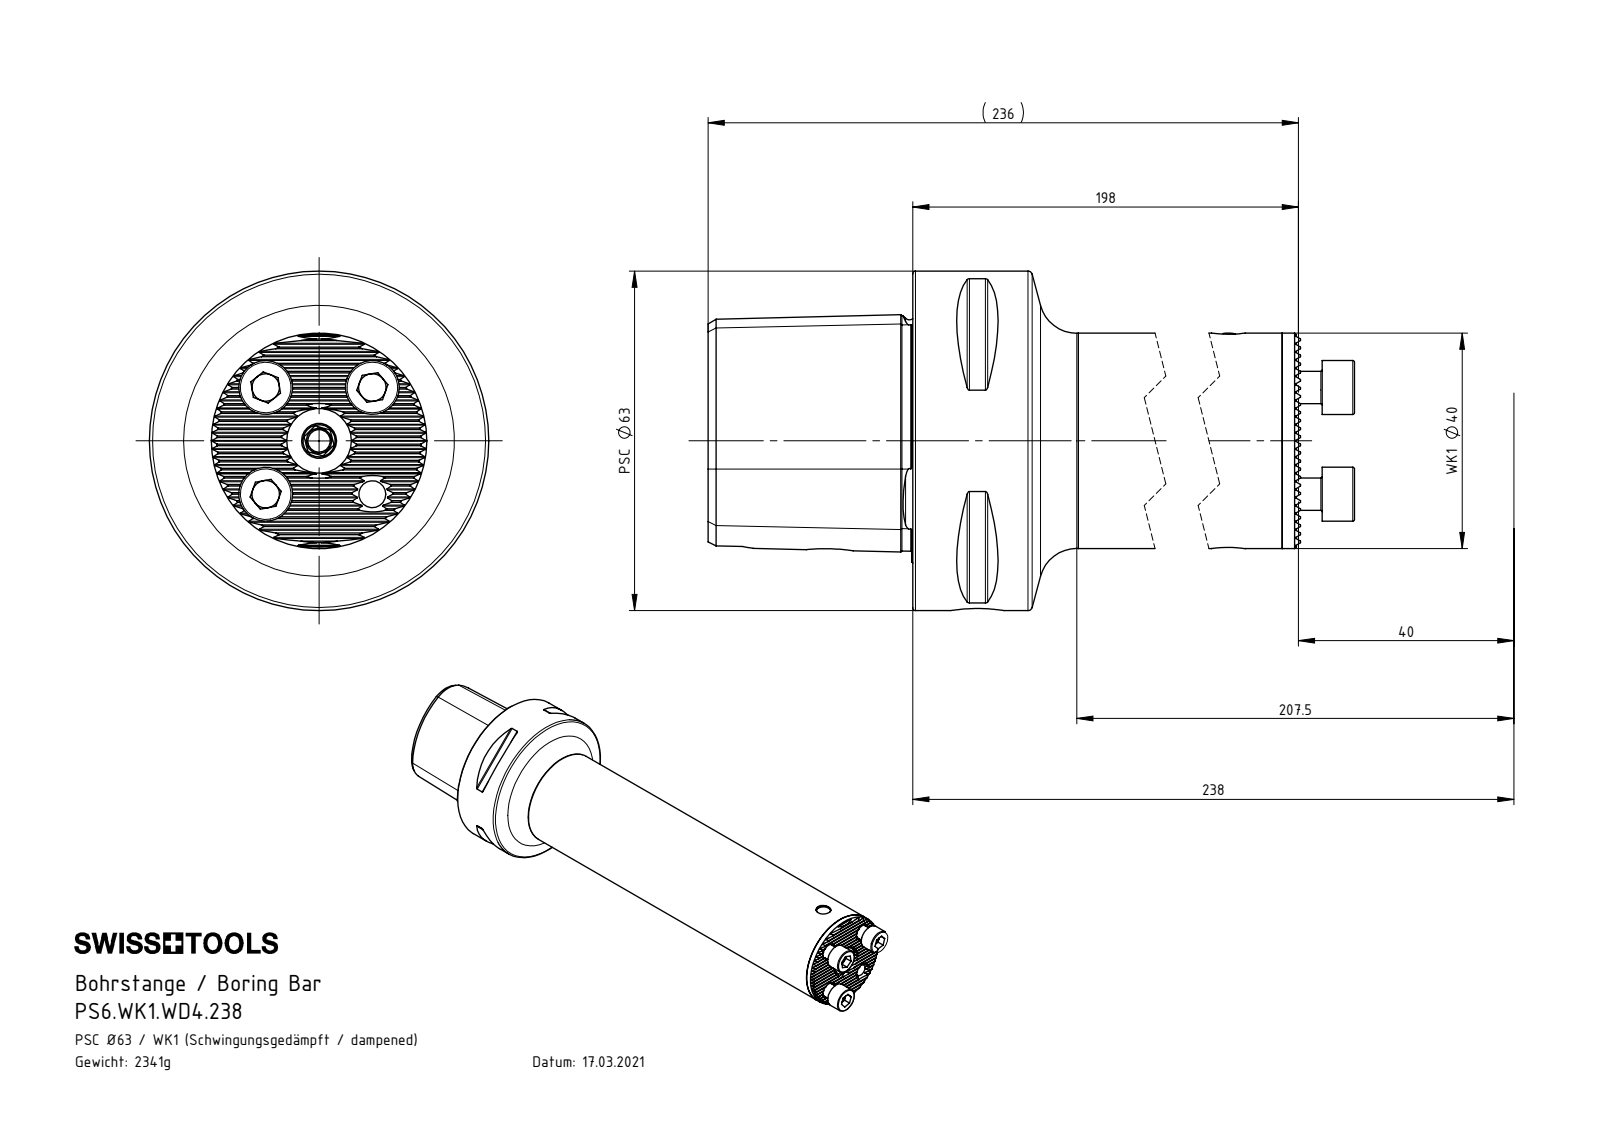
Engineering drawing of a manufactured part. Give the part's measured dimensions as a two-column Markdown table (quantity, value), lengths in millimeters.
| quantity | value |
| --- | --- |
| part name | ISO 4762 - M6 x 16; WD4-BG1.035.100; PS6.WK1.WD4.238; WD4-ER1.035.019_A (+8 more) |
| STEP written by | SolidWorks 2017 (AUTOMOTIVE_DESIGN) |
| units | millimeters |
| bodies | 16 solids, 532 faces (267 planar, 120 cylindrical, 145 other) |
| overall size | 246.4 × 63 × 63 |
| volume | 302 737 mm³ |
| surface area | 94 058 mm² |
| round holes (diameter × count) | 5 × 4, 6 × 2, 4.2 × 1, 7 × 1, 7.4 × 1, 8.1 × 1, 8.5 × 1, 10 × 1, 12 × 1, 14 × 1, 18 × 1, 21 × 1 |
| round bosses / shafts (diameter × count) | 10 × 3, 6 × 3, 63 × 1, 40 × 1, 35 × 1, 34.7 × 1, 34 × 1, 31.8 × 1 |
| partial cylindrical surfaces (radius × count) | 0.12 × 27, 0.5 × 8, 6 × 1 |
| main face-to-face distances | 6, 93.4, 6.2, 93.2, 87.2, 178, 83.75, 171.15, 87.4, 94.25 |
| hole center spacings | 14, 19.8, 28, 27.5, 173, 200.5 |
